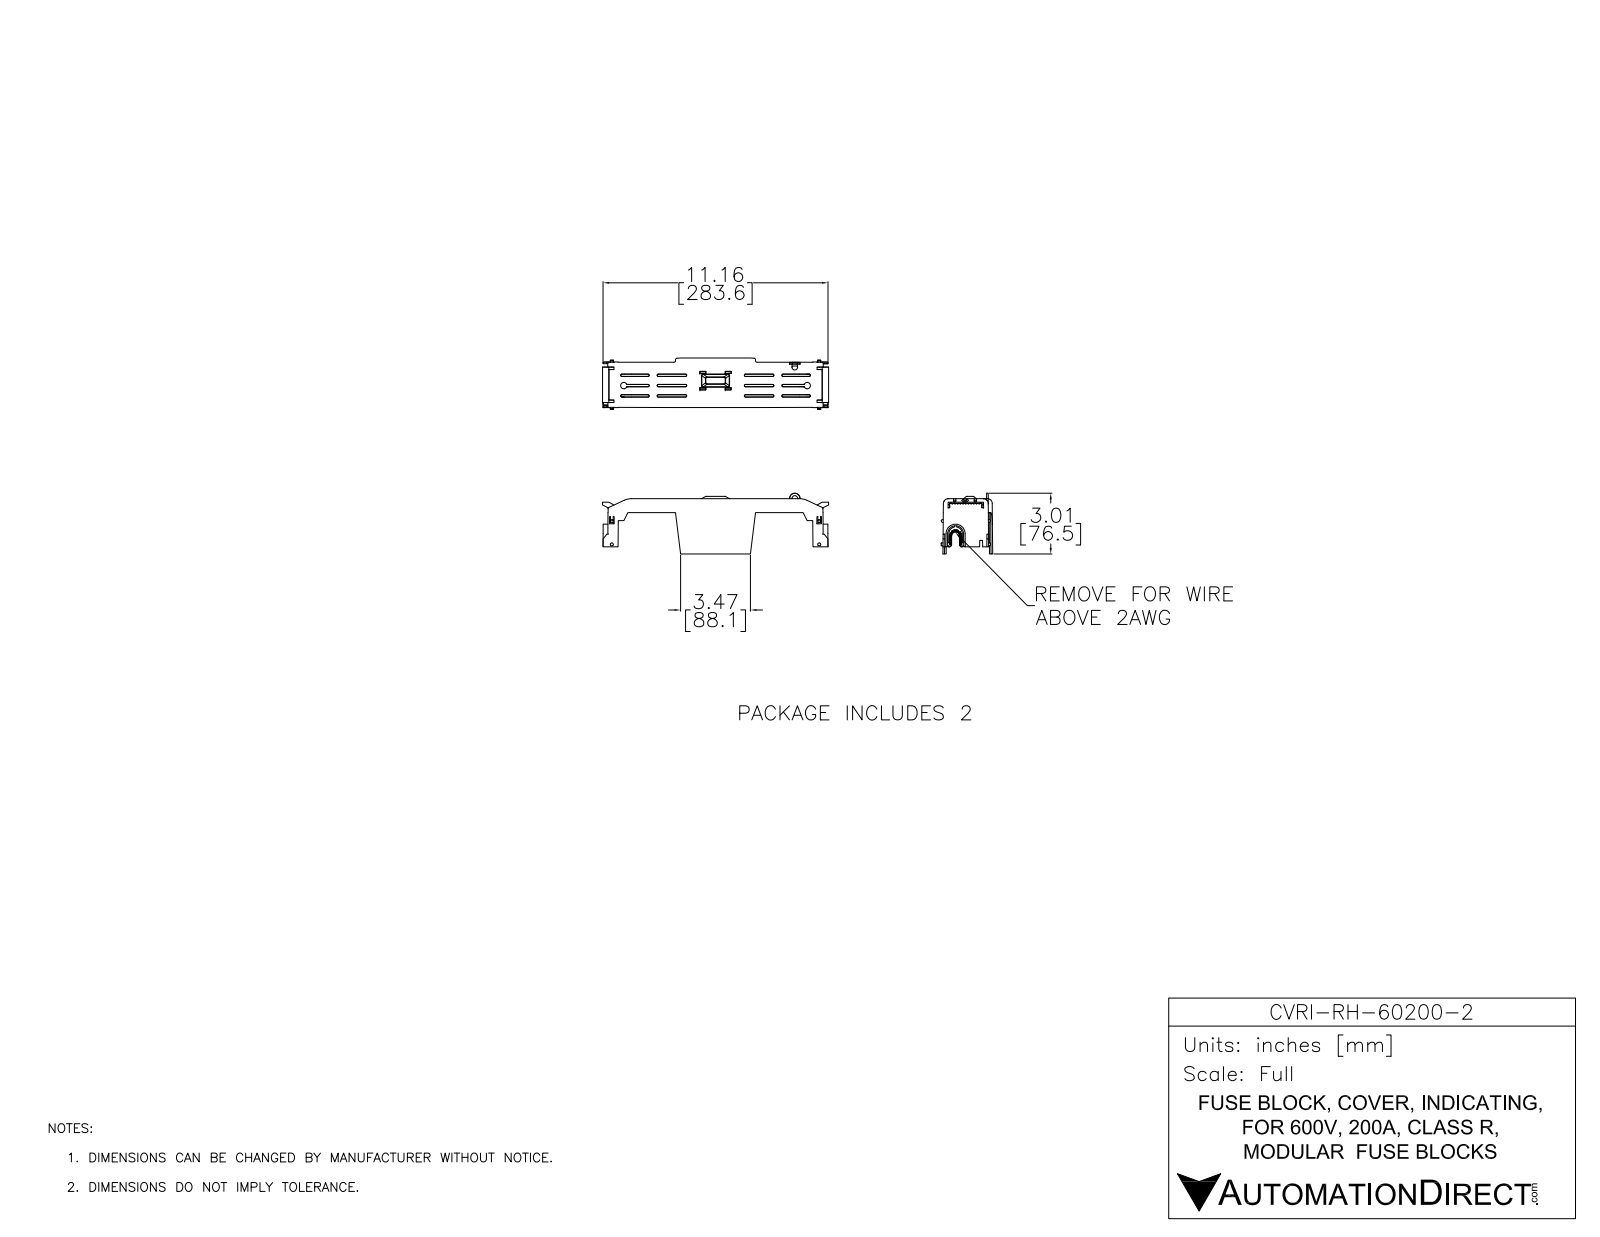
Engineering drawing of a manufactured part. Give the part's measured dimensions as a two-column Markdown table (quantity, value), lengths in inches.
| quantity | value |
| --- | --- |
| part name | CVRI-RH-60200-2 |
| STEP written by | SolidWorks 2017 (AUTOMOTIVE_DESIGN) |
| units | inches |
| bodies | 1 solid, 1446 faces (937 planar, 106 cylindrical, 403 other) |
| overall size | 11.215 × 3.012 × 2.553 |
| volume | 5.503 in³ |
| surface area | 149.2 in² |
| round holes (diameter × count) | 0.276 × 1 |
| partial cylindrical surfaces (radius × count) | 0.039 × 16, 0.118 × 8, 0.157 × 7, 0.236 × 7, 0.079 × 6, 0.01 × 2, 0.02 × 2, 0.197 × 2 |
| main face-to-face distances | 0.079, 0.197, 0.118, 0.276, 0.512, 0.803, 0.624, 1.681, 1.76, 1.267 |
